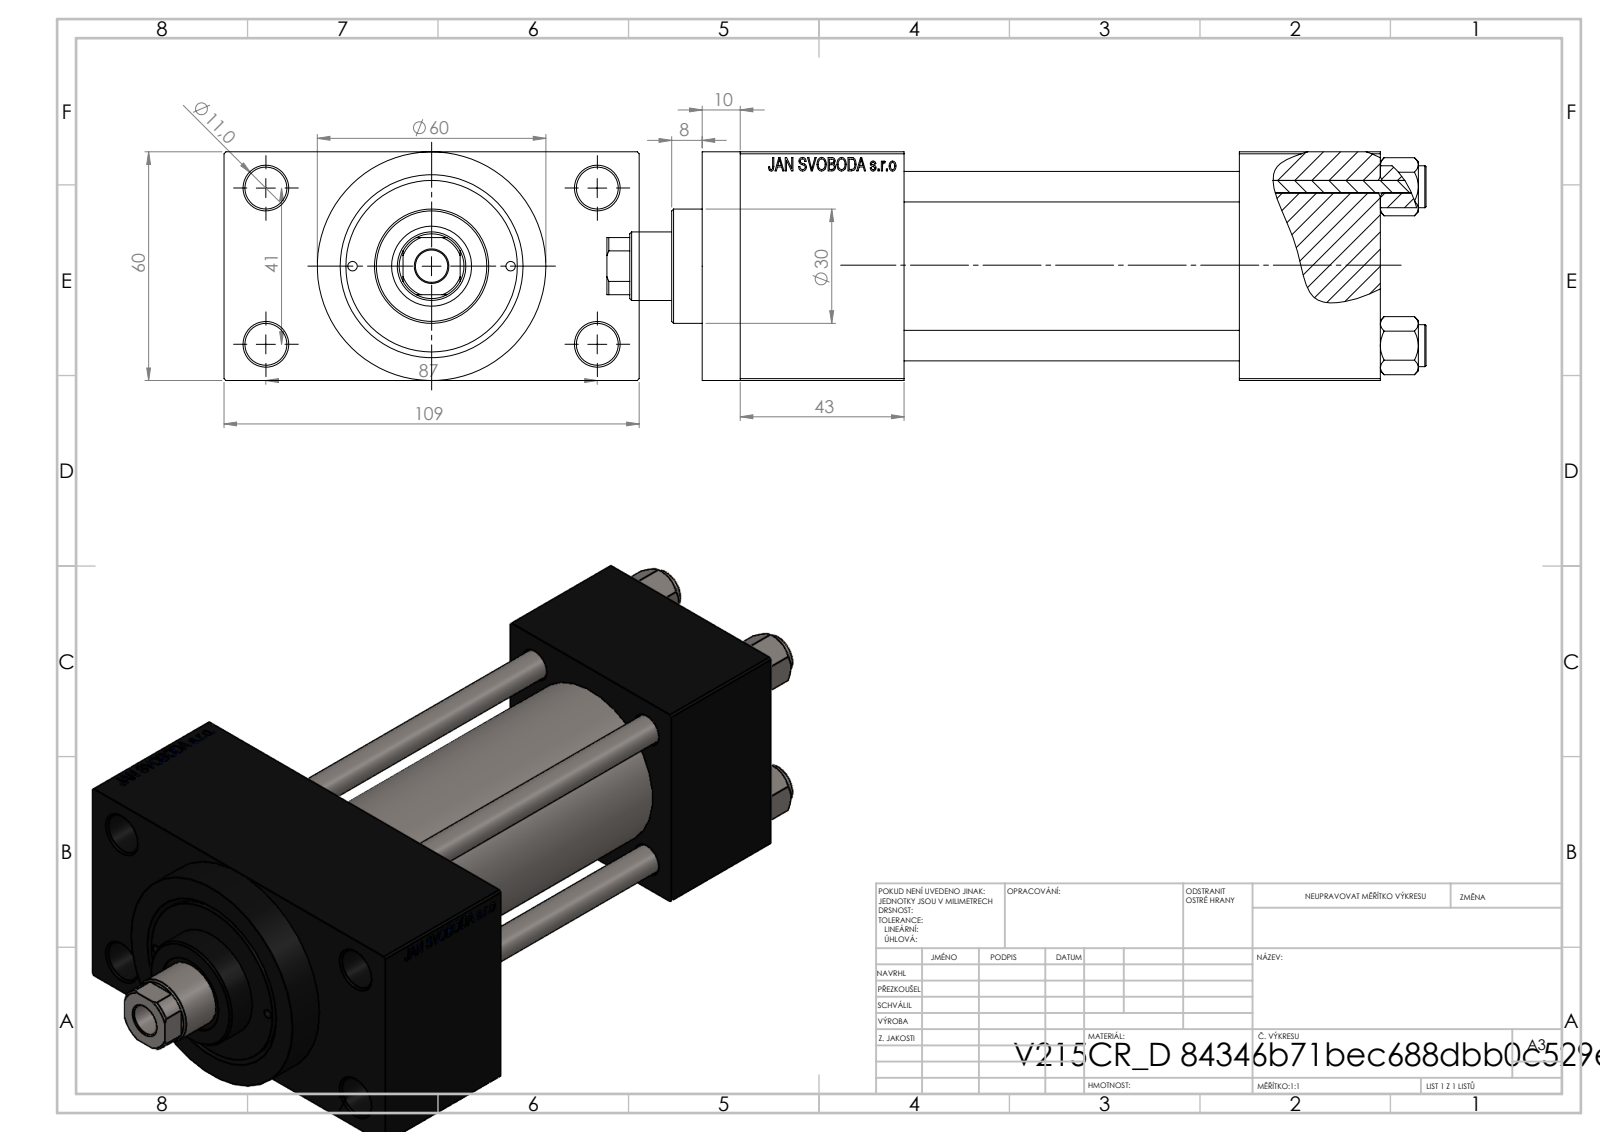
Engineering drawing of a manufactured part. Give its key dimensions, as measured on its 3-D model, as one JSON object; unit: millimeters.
{"part_name": "NUT_M5_D; V215CR_D_Body; V215CR_VCP_D; V215CR_D_TYCINKA (+1 more)", "step_written_by": "SolidWorks 2019 (CONFIG_CONTROL_DESIGN)", "units": "millimeters", "bodies": {"solids": 11, "faces": 1112, "planar": 500, "cylindrical": 92, "other": 520}, "overall_size": [215, 109, 60], "volume_mm3": 538134, "surface_area_mm2": 135321, "round_holes": [[8, 4], [11, 4], [2.5, 2], [7, 2], [16.66, 2], [24, 2], [8.5, 1], [18, 1], [21, 1], [31, 1], [40, 1], [45, 1]], "round_bosses_or_shafts": [[11, 4], [60, 1], [46, 1], [30, 1]], "partial_cylinders_radius": [[8.5, 1]], "face_to_face_distances": [60, 88, 24.5, 84.5, 37, 125, 168, 131, 43, 134.74], "hole_center_spacings": [20.85, 22.65, 29.49, 30.62, 41.7, 46.53, 47.15, 48.09]}
